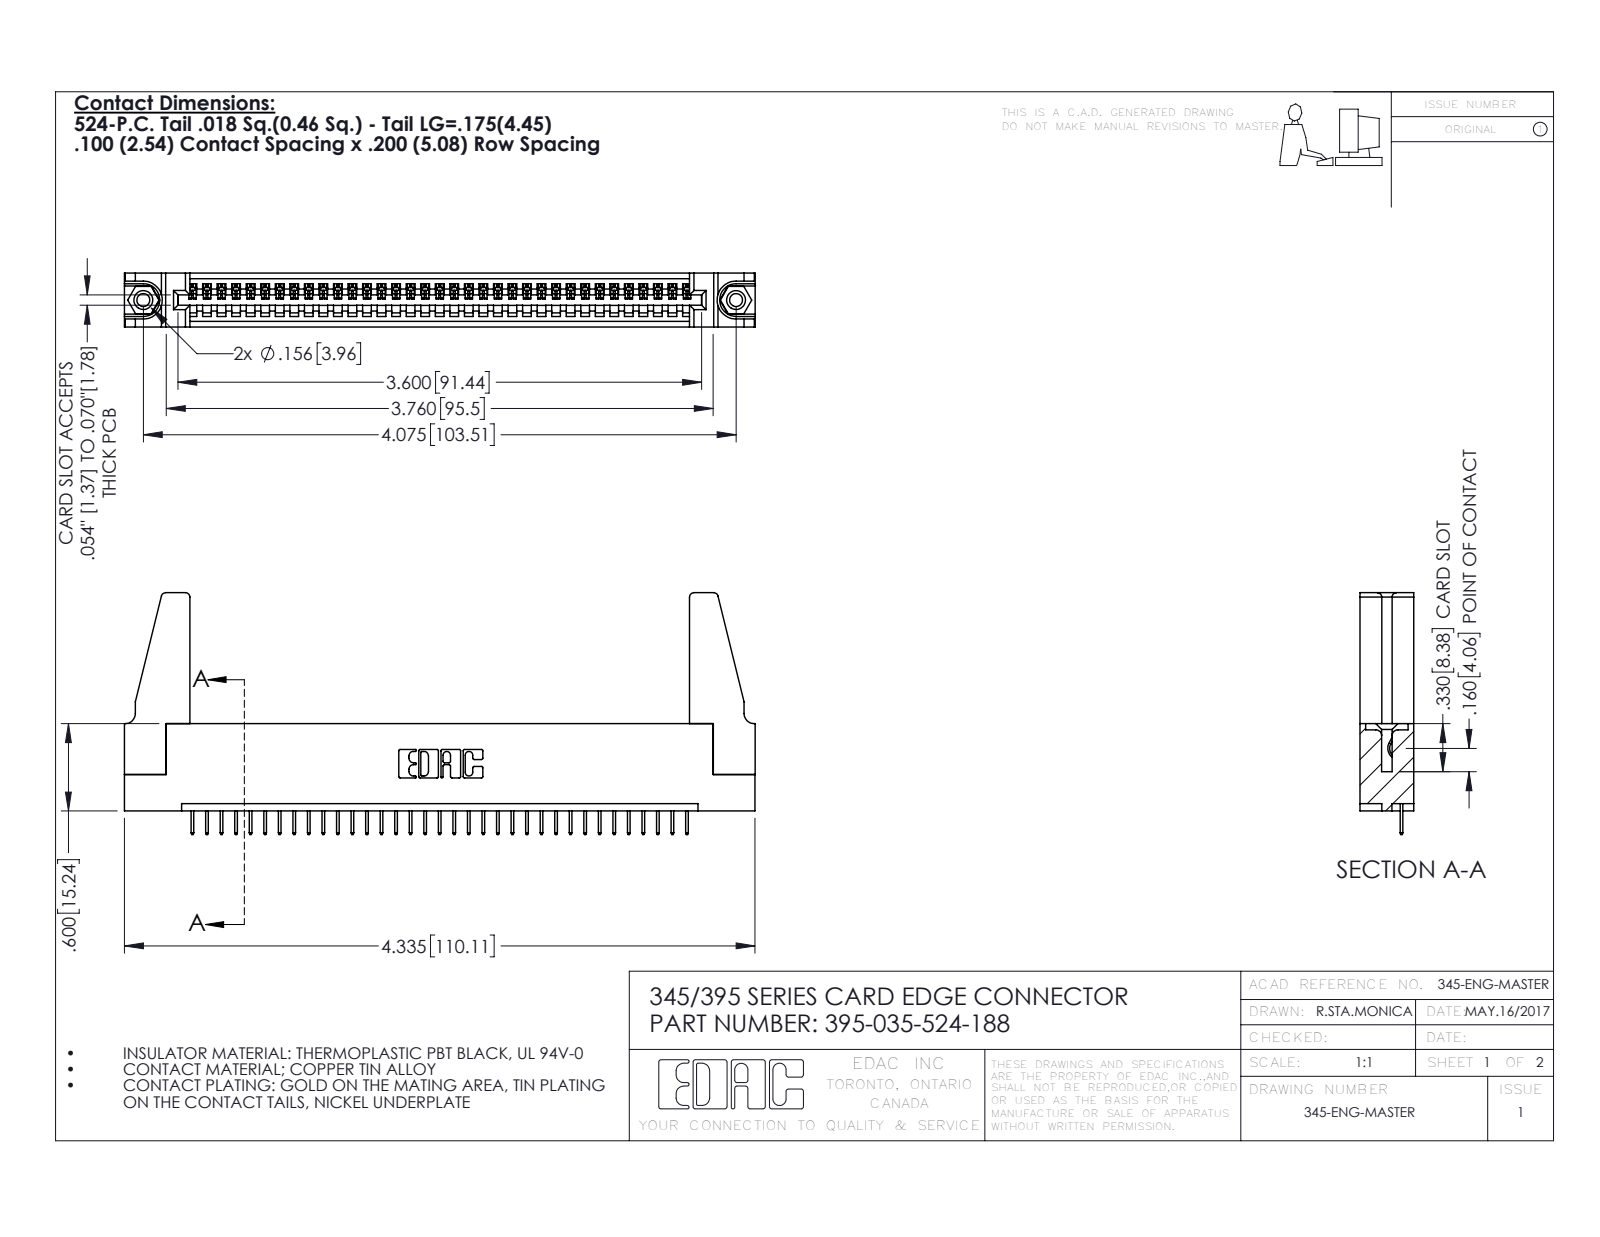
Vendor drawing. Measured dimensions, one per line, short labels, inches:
name: 395-035-524-188; 345-220-078_345-220-088; 345-292-001_345-293-124; 345-250-001_345-250-001-102 (+1 more)
written by: SolidWorks 2016 (CONFIG_CONTROL_DESIGN)
unit: in
bodies: 40 solids, 2420 faces (1762 planar, 642 cylindrical, 16 other)
size: 4.336 × 1.662 × 0.37
volume: 0.825 in³; area: 25.16 in²
holes: 2× ⌀0.089, 2× ⌀0.125, 2× ⌀0.156, 1× ⌀0.064
bosses: 2× ⌀0.155
rounds: 70× R0.006, 22× R0.01, 8× R0.03, 6× R0.007, 6× R0.031, 3× R0.026, 2× R0.031, 2× R0.04
face distances: 0.072, 0.37, 0.298, 0.2, 0.098, 0.272, 0.025, 0.225, 0.072, 0.149
hole spacings: 0.27, 3.839, 4.075
